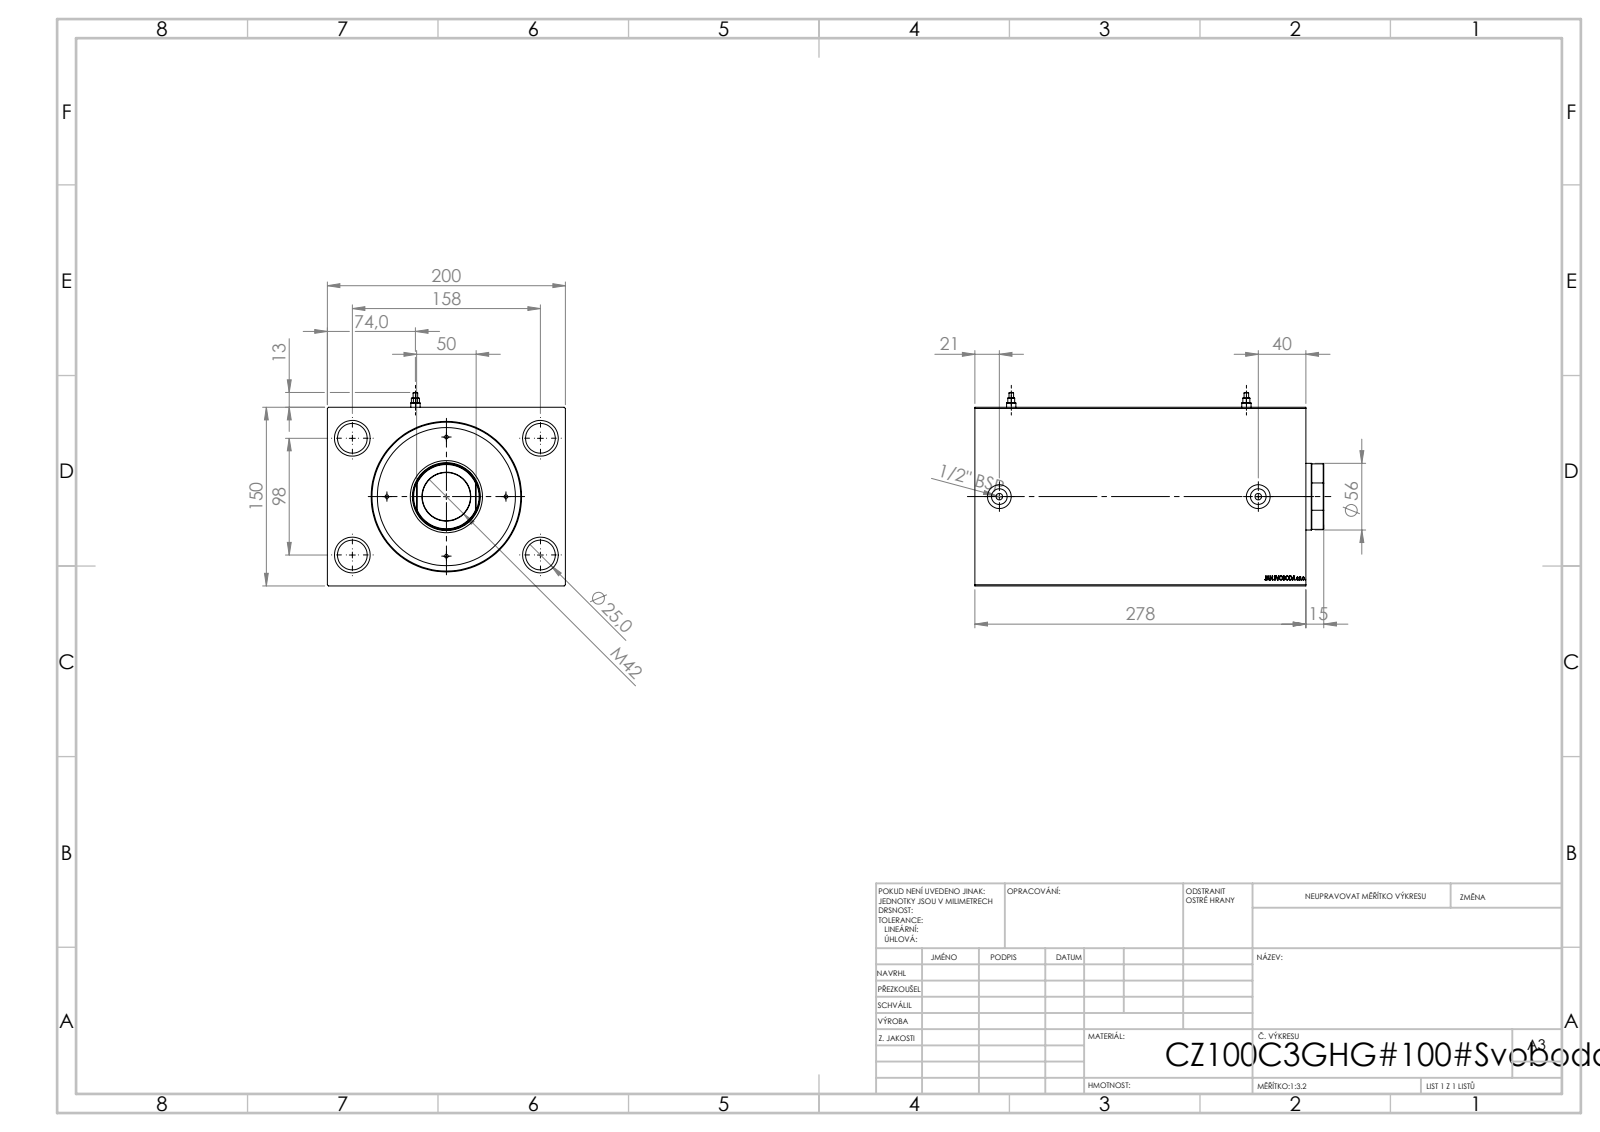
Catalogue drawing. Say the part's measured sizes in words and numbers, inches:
The part is named "V500CZ_B_VC; Zatka_Cushioning3; V500CZ_C; V500CZ_VCP_C". Its 3-D file was written by "SolidWorks 2019 (CONFIG_CONTROL_DESIGN)". It is 5 solids with 934 faces: 432 planar, 82 cylindrical and 420 other. Overall it measures 11.535 by 7.874 by 6.398 inches. Its volume is 437.5 cubic inches and its surface area 829.6 square inches. Round holes: 4 of diameter 0.118, 4 of diameter 0.984, 4 of diameter 1.181, 2 of diameter 0.071, 2 of diameter 0.217, 2 of diameter 0.315, 2 of diameter 0.518, 2 of diameter 0.787, 1 of diameter 1.417, 1 of diameter 1.594, 1 of diameter 2.205, 1 of diameter 2.244. Round bosses or shafts: 2 of diameter 0.307, 2 of diameter 0.15, 1 of diameter 4.567. Partial cylindrical surfaces (rounded edges, fillets, slot ends): 1 of radius 1.083. The main face-to-face distances are 5.906, 7.874, 10.945, 9.634, 1.311, 0.591, 9.043, 10.354, 4.528, 3.937. The hole center spacings are 1.969, 2.242, 2.784, 3.111, 3.66, 4.987, 5.433, 3.858.
